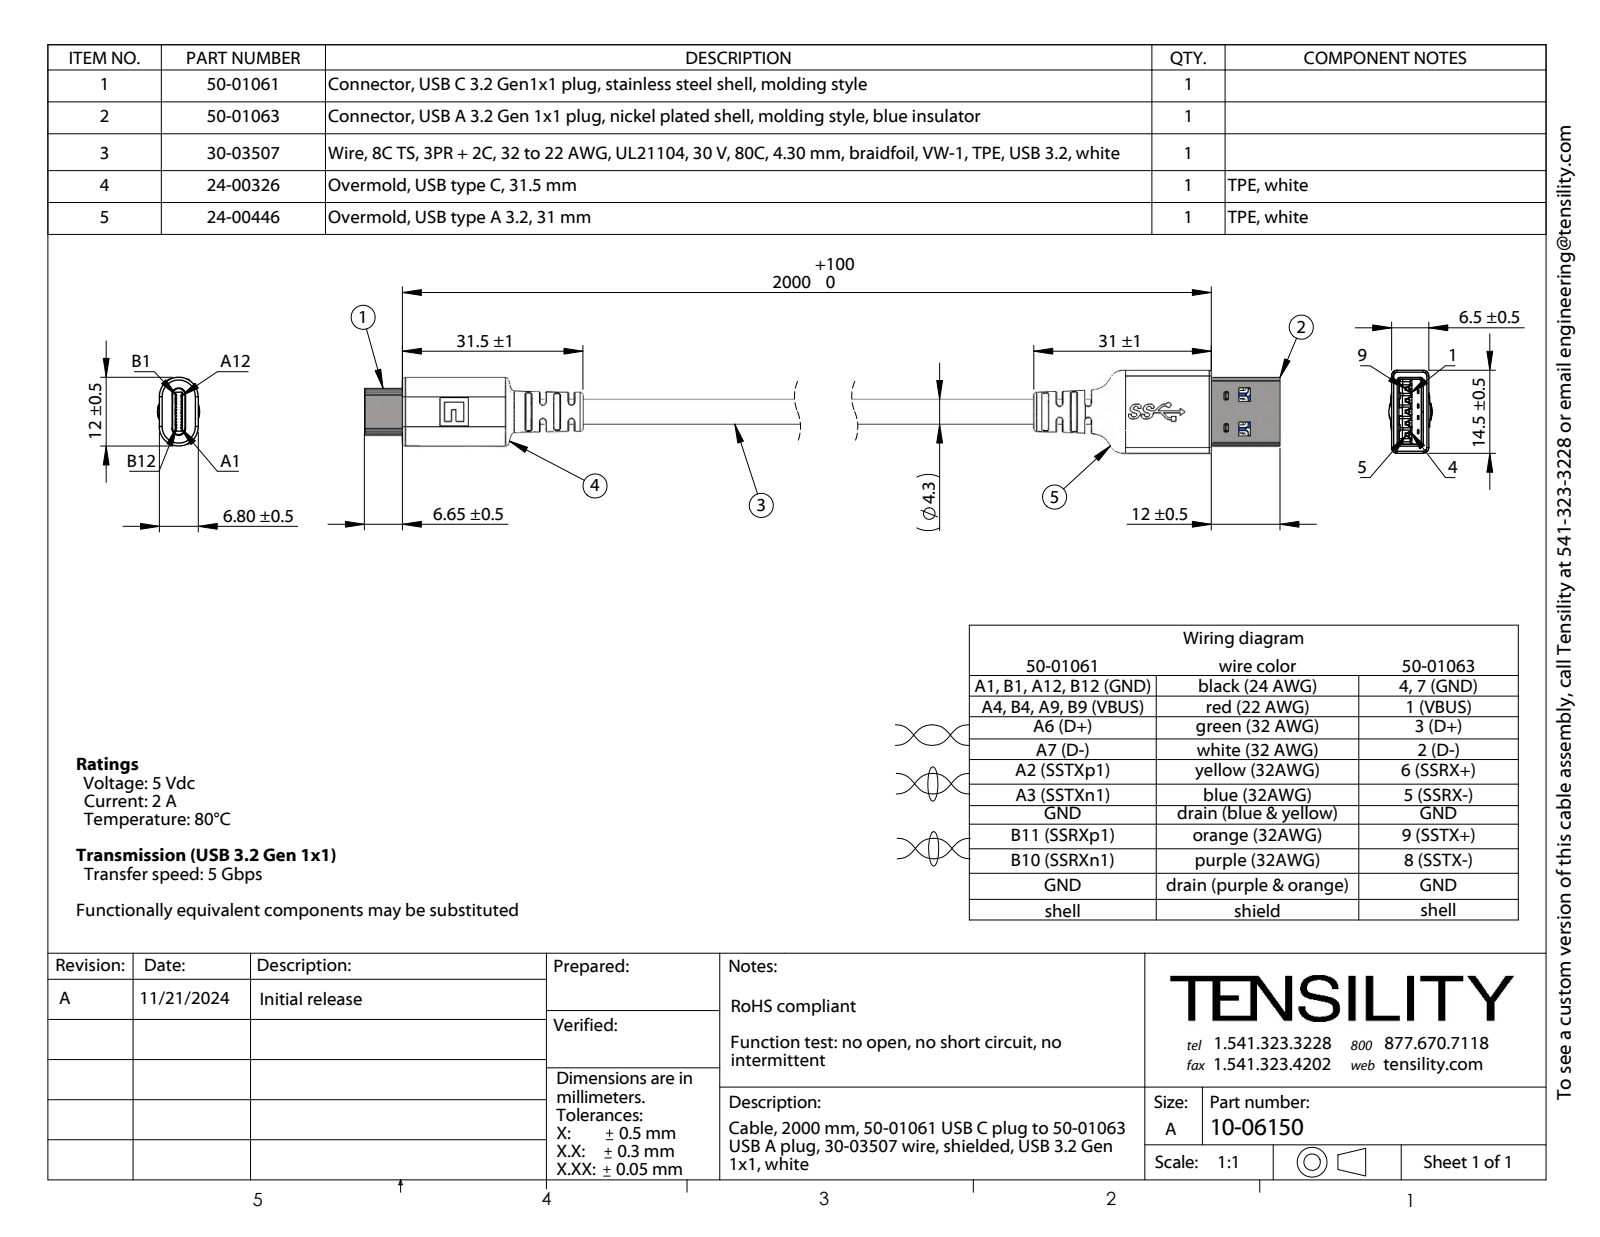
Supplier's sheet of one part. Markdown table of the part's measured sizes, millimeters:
| quantity | value |
| --- | --- |
| part name | 50-01063_shell; 30-03507; 50-01063_pin1; 50-01063_insulator (+8 more) |
| STEP written by | SolidWorks 2021 (CONFIG_CONTROL_DESIGN) |
| units | millimeters |
| bodies | 131 solids, 2476 faces (1293 planar, 809 cylindrical, 374 other) |
| overall size | 211.15 × 14.5 × 7.54 |
| volume | 5 774 mm³ |
| surface area | 29 800 mm² |
| round holes (diameter × count) | 0.87 × 1, 3.23 × 1, 3.25 × 1, 3.35 × 1 |
| round bosses / shafts (diameter × count) | 0.6 × 4, 0.75 × 2, 0.55 × 2, 0.45 × 2, 4.3 × 1, 1.66 × 1, 1 × 1, 0.9 × 1 |
| partial cylindrical surfaces (radius × count) | 0.1 × 30, 0.2 × 24, 0.5 × 20, 0.3 × 13, 0.4 × 10, 0.25 × 9, 0.35 × 7, 0.6 × 7 |
| main face-to-face distances | 0.89, 4.25, 0.9, 0.88, 2.5, 0.35, 6.5, 3.1, 1.27, 0.97 |
| hole center spacings | 0.32, 0.56, 0.71, 0.92, 0.63, 0.64, 0.78, 0.95 |
